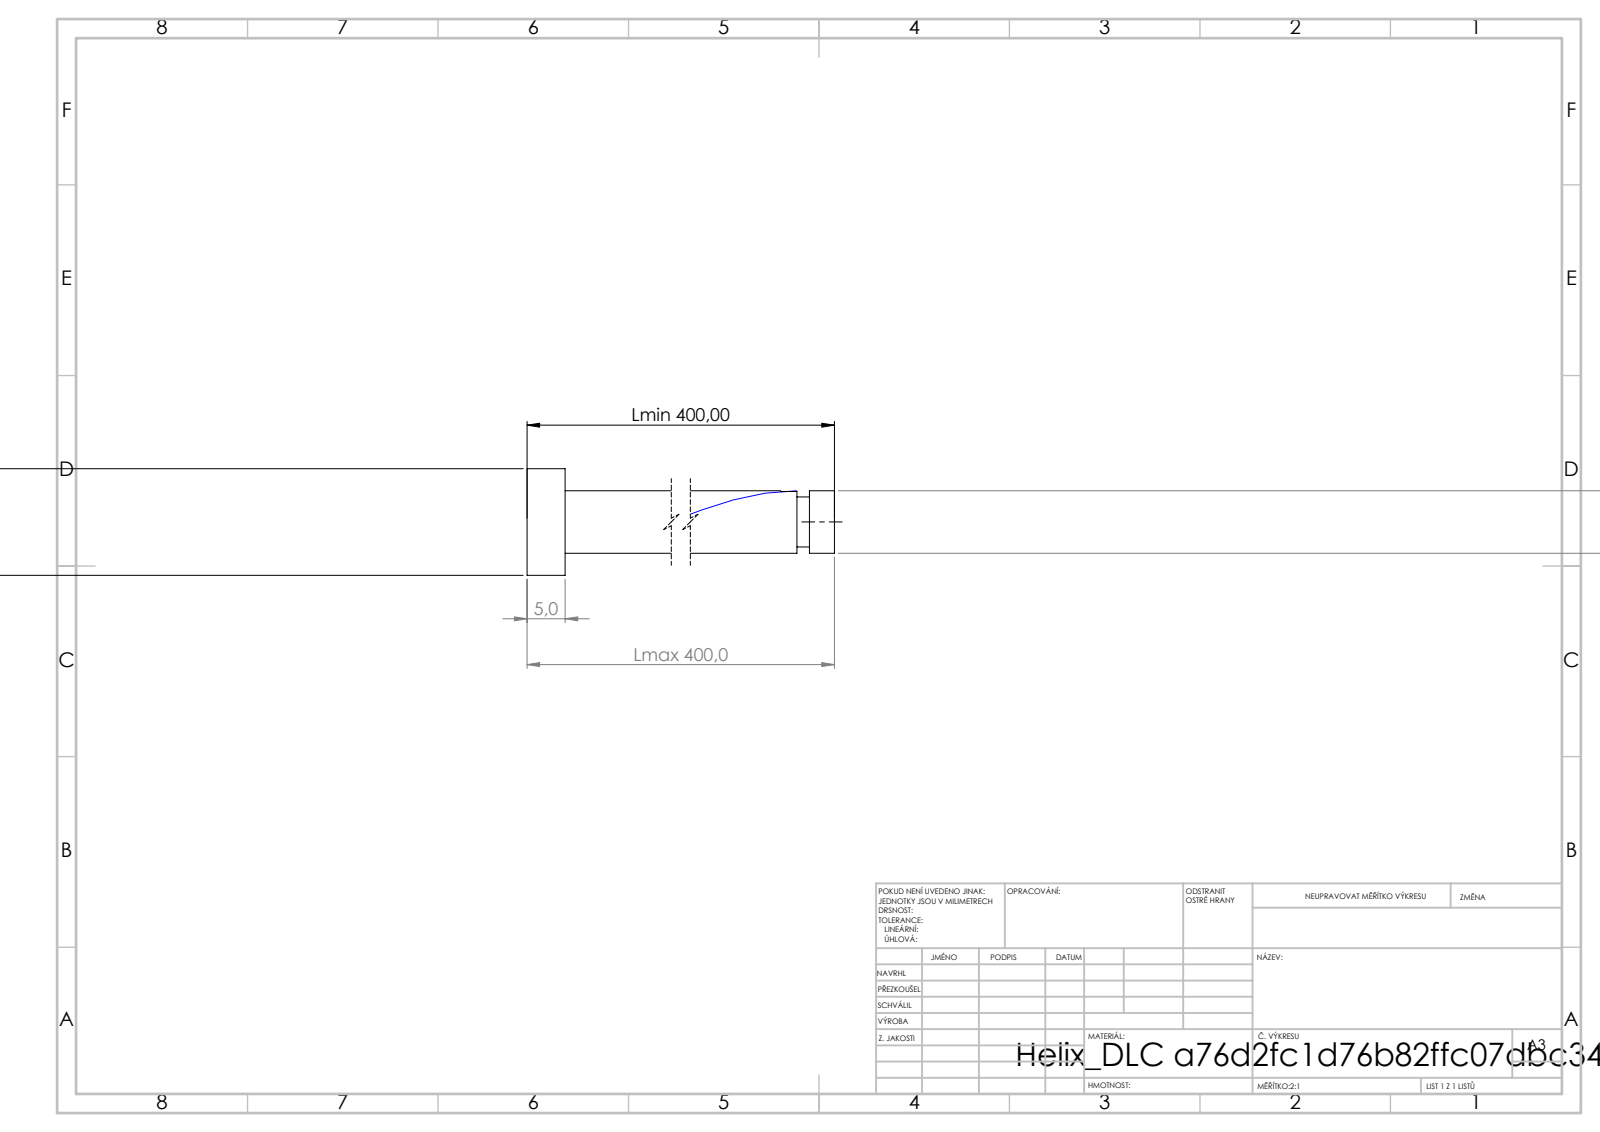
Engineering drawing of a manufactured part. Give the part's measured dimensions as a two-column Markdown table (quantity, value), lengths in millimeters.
| quantity | value |
| --- | --- |
| STEP written by | SolidWorks 2019 (CONFIG_CONTROL_DESIGN) |
| units | millimeters |
| bodies | 1 solid, 21 faces (6 planar, 14 cylindrical, 1 other) |
| overall size | 400 × 14 × 14 |
| volume | 21 396 mm³ |
| surface area | 10 903 mm² |
| round bosses / shafts (diameter × count) | 14 × 1, 8.2 × 1, 6.56 × 1 |
| main face-to-face distances | 5, 400, 395, 396.71, 391.71, 3.29, 395.07, 390.07, 1.64, 4.93 |
